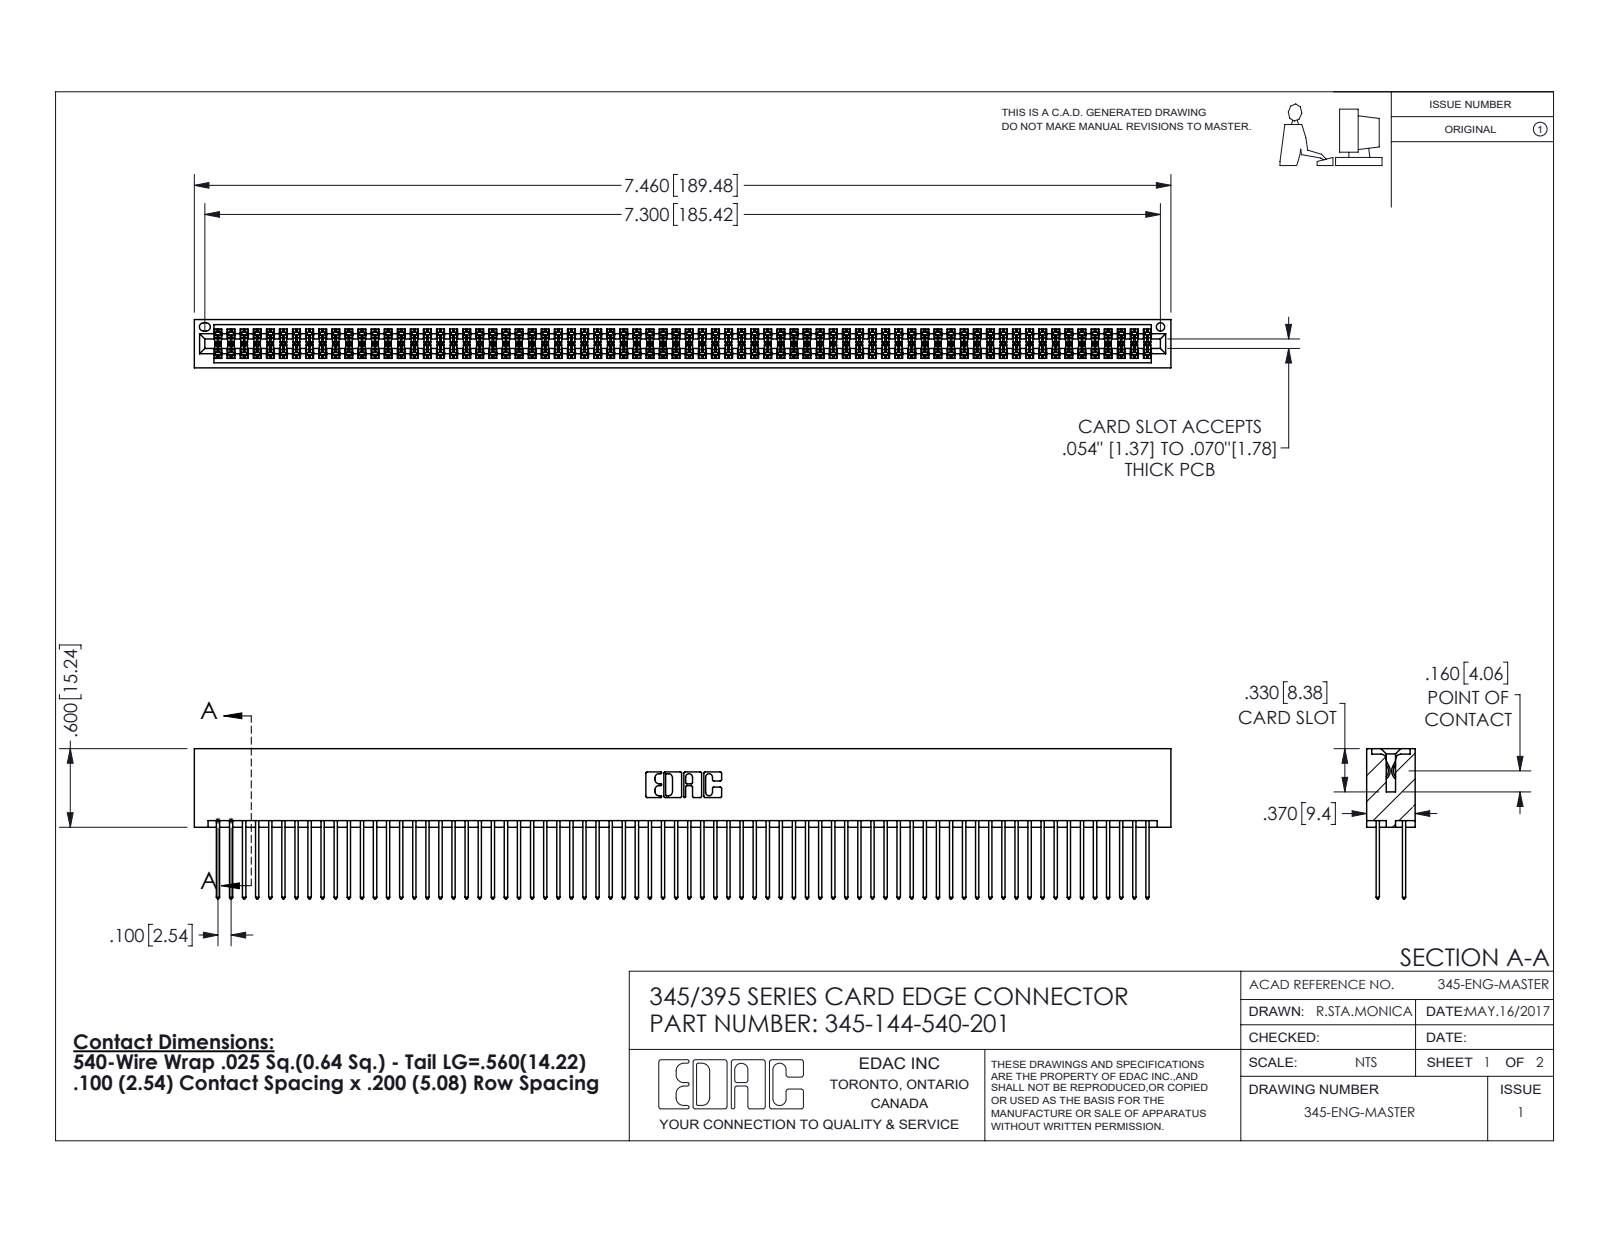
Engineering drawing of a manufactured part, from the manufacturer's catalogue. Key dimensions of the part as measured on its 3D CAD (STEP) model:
Part name (STEP PRODUCT): 345-292-001_345-293-140; 345 Part_No Mounting Lugs; 345-144-540-201
STEP written by: SolidWorks 2016 (CONFIG_CONTROL_DESIGN)
Units: inches
Bodies: 145 solids, 7318 faces (4828 planar, 2490 cylindrical, 0 other)
Overall size (bounding box): 7.46 × 1.147 × 0.37
Volume: 1.211 in³ · Surface area: 50.77 in²
Round holes (diameter × count): ⌀0.064 ×1
Partial cylindrical surfaces — rounded edges, fillets, slot ends (radius × count): R0.006 ×216, R0.01 ×144, R0.01 ×22, R0.007 ×6, R0.031 ×6, R0.026 ×3, R0.014 ×2, R0.019 ×2
Main face-to-face distances: 0.298, 0.072, 0.2, 0.098, 0.272, 0.025, 0.225, 0.37, 0.175, 0.149
